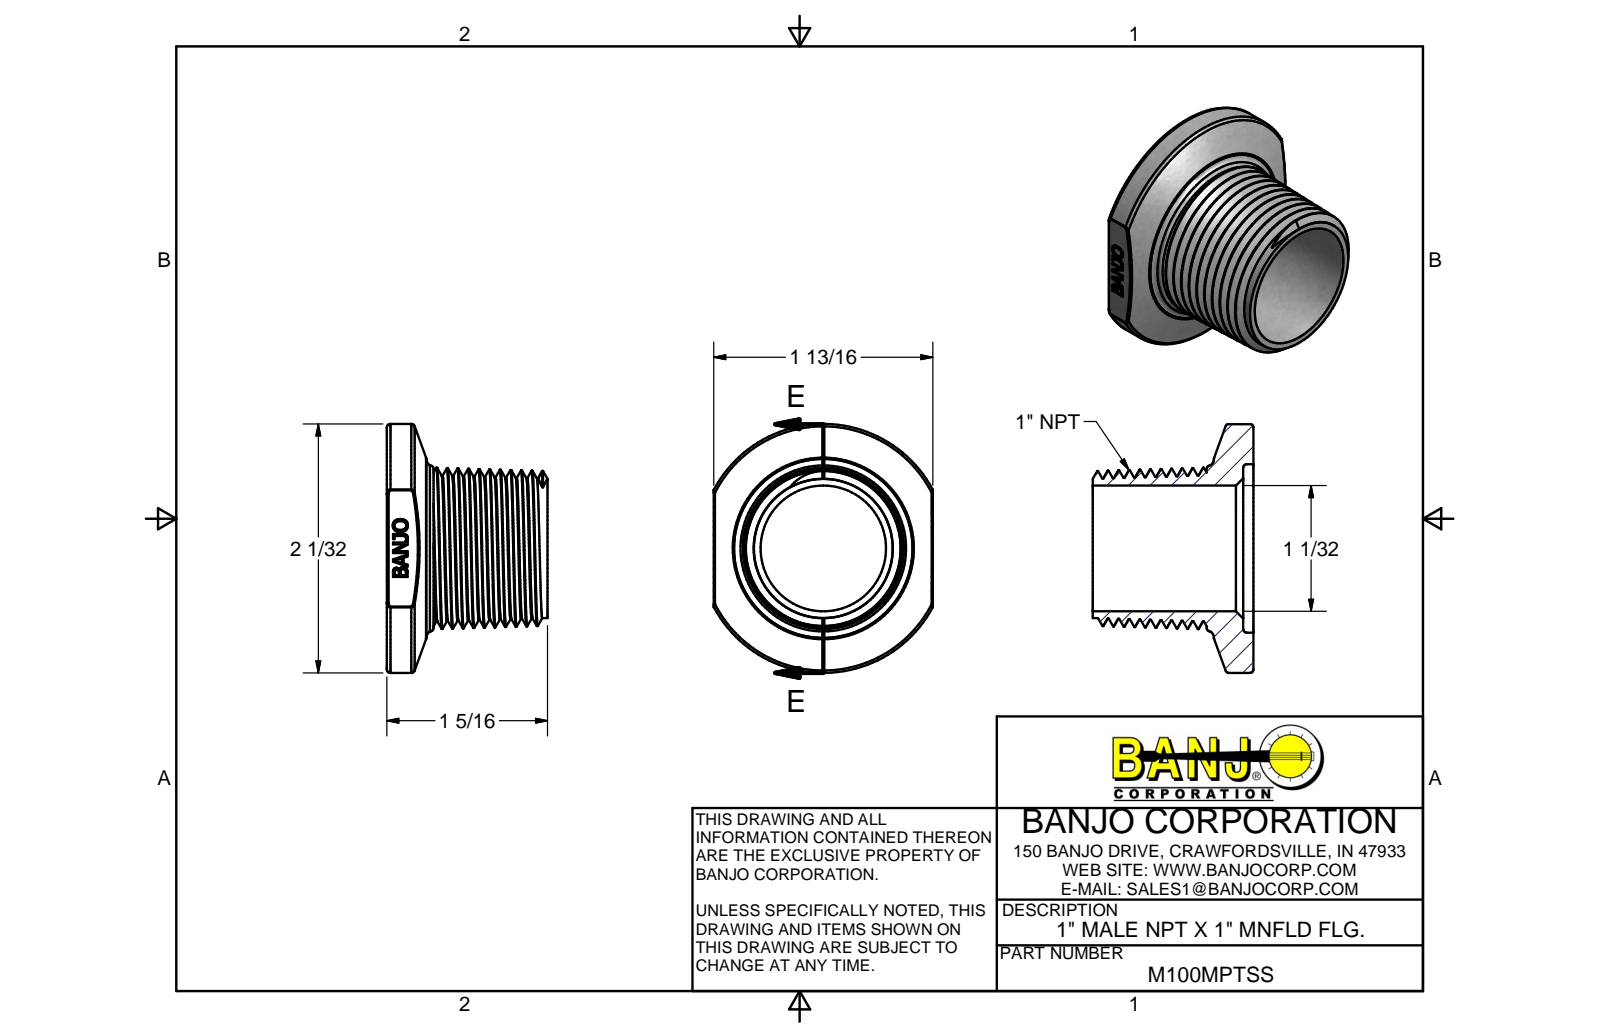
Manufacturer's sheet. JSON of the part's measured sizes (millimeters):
{"part_name": "M100MPTSS", "step_written_by": "Autodesk Inventor 2014 (AUTOMOTIVE_DESIGN)", "units": "millimeters", "bodies": {"solids": 1, "faces": 261, "planar": 126, "cylindrical": 11, "other": 124}, "overall_size": [51.82, 45.72, 33.53], "volume_mm3": 15971, "surface_area_mm2": 10895, "round_holes": [[26.16, 1], [35.05, 1]], "partial_cylinders_radius": [[0.38, 6], [8.87, 1], [25.91, 1]], "face_to_face_distances": [2.13, 31.4, 33.53, 45.72, 7.63, 23.77, 9.76, 0.76, 44.96, 44.2]}
